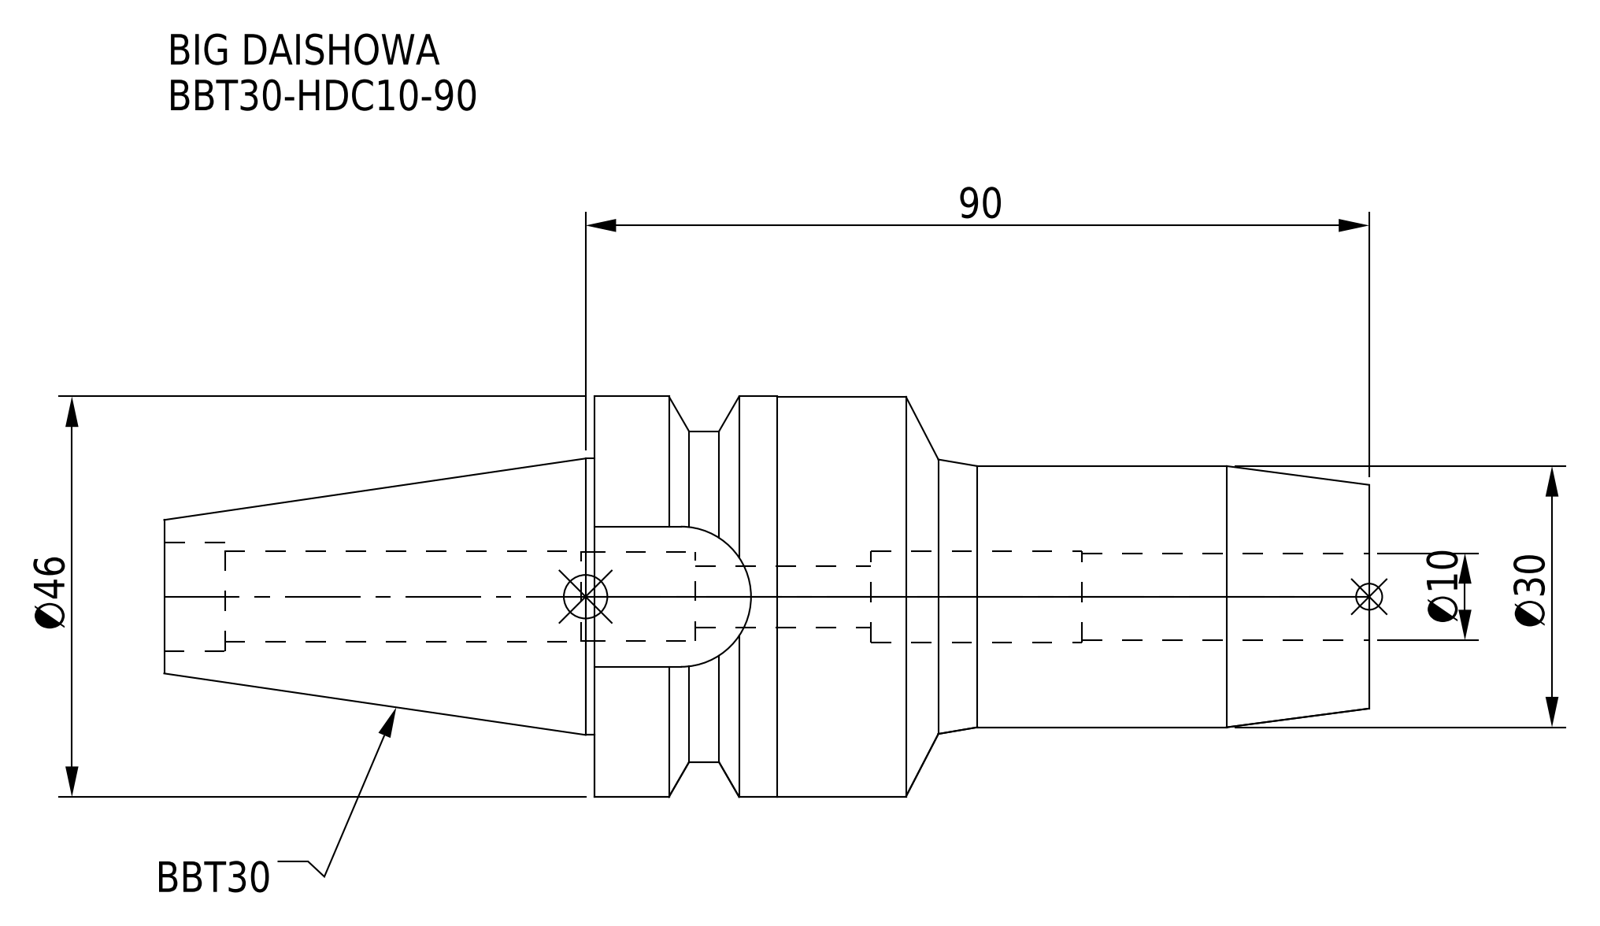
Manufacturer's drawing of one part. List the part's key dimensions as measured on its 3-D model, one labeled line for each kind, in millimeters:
Part name (STEP PRODUCT): BBT30-HDC10-90
STEP written by: CREO PARAMETRIC BY PTC INC, 2016380 (AUTOMOTIVE_DESIGN)
Units: millimetres
Bodies: 1 solid, 55 faces (15 planar, 28 cylindrical, 12 other)
Overall size (bounding box): 138.4 × 46 × 46
Volume: 105 435 mm³ · Surface area: 21 043 mm²
Round holes (diameter × count): ⌀7 ×1, ⌀10 ×1, ⌀10.2 ×1, ⌀10.4 ×1, ⌀10.5 ×1, ⌀12.5 ×1
Round bosses / shafts (diameter × count): ⌀46 ×1, ⌀45.9 ×1, ⌀31.75 ×1, ⌀30 ×1
Partial cylindrical surfaces — rounded edges, fillets, slot ends (radius × count): R8.05 ×1, R19 ×1
Main face-to-face distances: 89, 32.6, 138.4, 49.4, 16.1, 57.2, 31.8, 81.2, 77.4, 20.2
